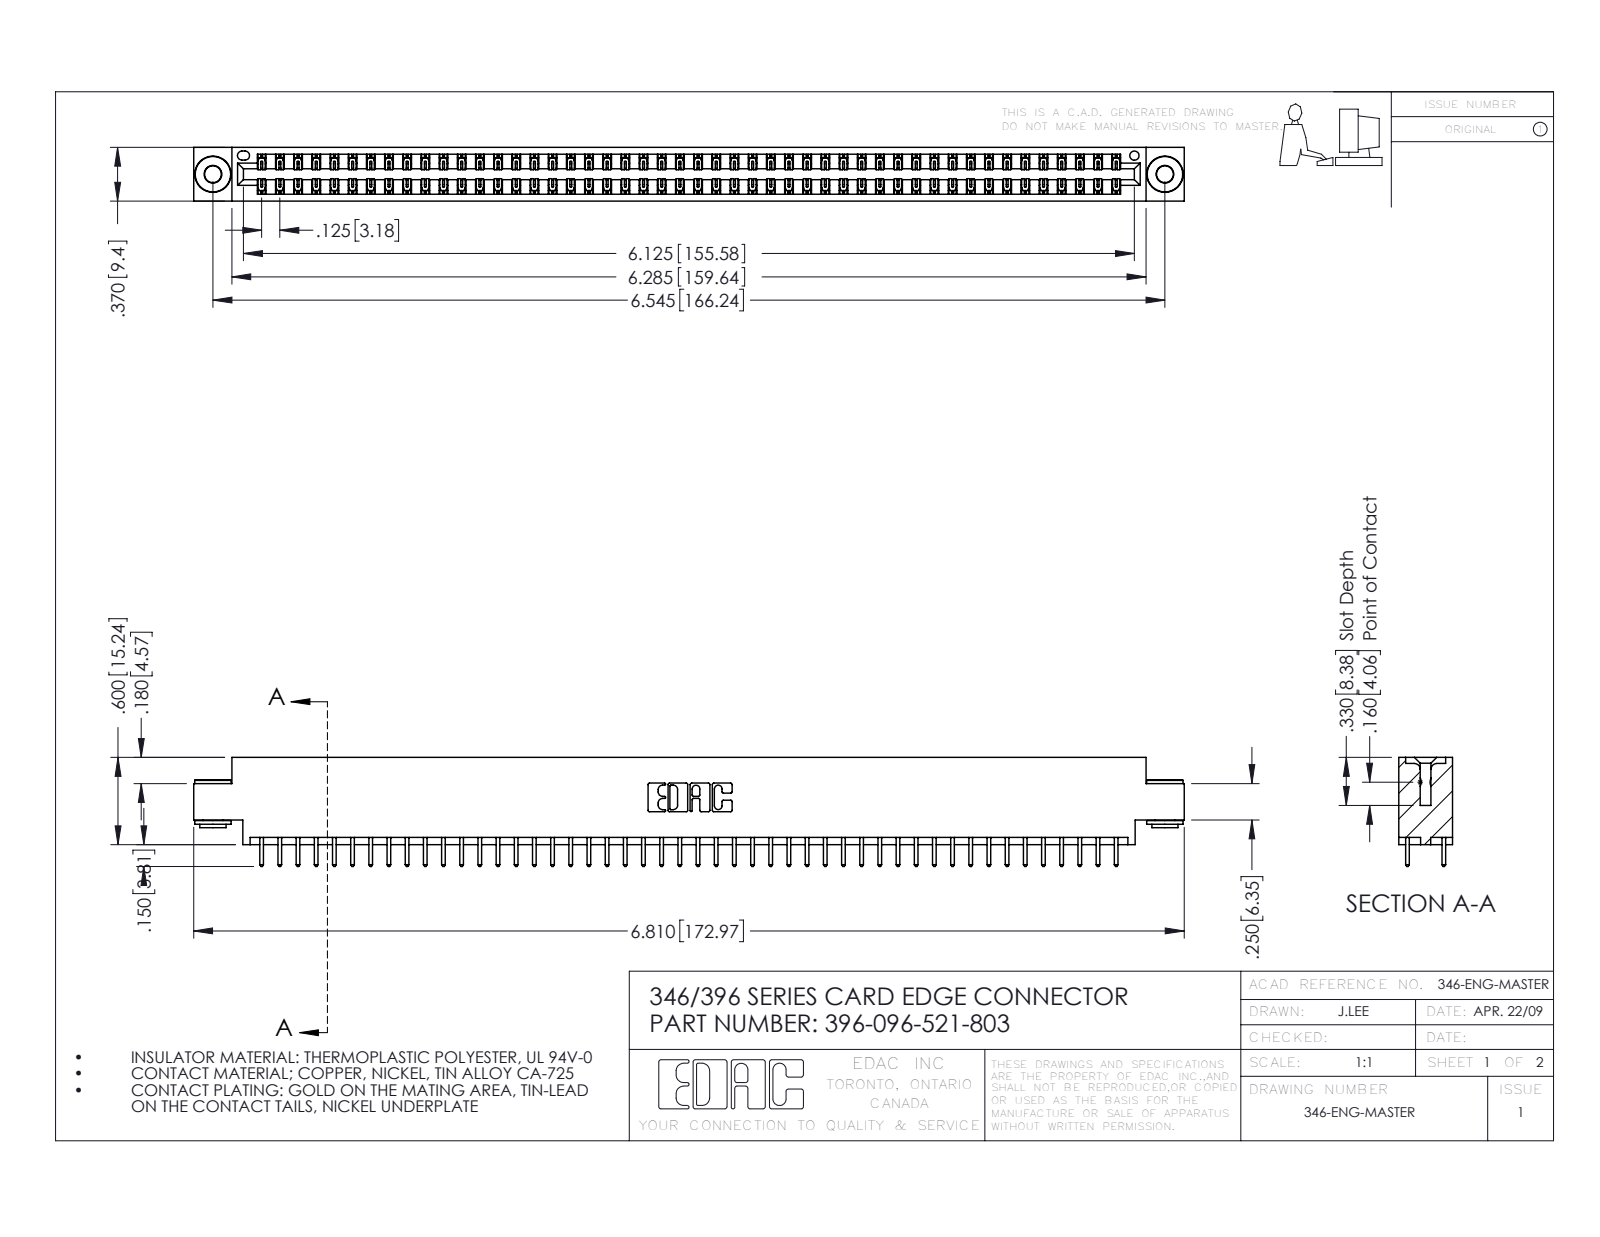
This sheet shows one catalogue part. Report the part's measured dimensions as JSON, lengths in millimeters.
{"part_name": "346 Part_0.170 Offset - 0.156 Dia-TH; 396-096-521-803; 345-250-002_345-250-002-102; 345-292-001_345-293-121", "step_written_by": "SolidWorks 2016 (CONFIG_CONTROL_DESIGN)", "units": "millimeters", "bodies": {"solids": 99, "faces": 5156, "planar": 3450, "cylindrical": 1698, "other": 8}, "overall_size": [173, 19.1, 9.4], "volume_mm3": 16730, "surface_area_mm2": 23230, "round_holes": [[2.9, 2], [4, 2], [1.6, 1]], "round_bosses_or_shafts": [[6.4, 2], [4.6, 2], [3.5, 2]], "partial_cylinders_radius": [[0.2, 144], [0.3, 96], [0.3, 22], [0.2, 6], [0.8, 6], [0.7, 3], [0.4, 2], [0.6, 2]], "face_to_face_distances": [1.2, 8.2, 9.4, 6.4, 0.6, 1.8, 7.6, 7, 3.8, 5.6], "hole_center_spacings": [6.2, 160.9, 166.2]}
